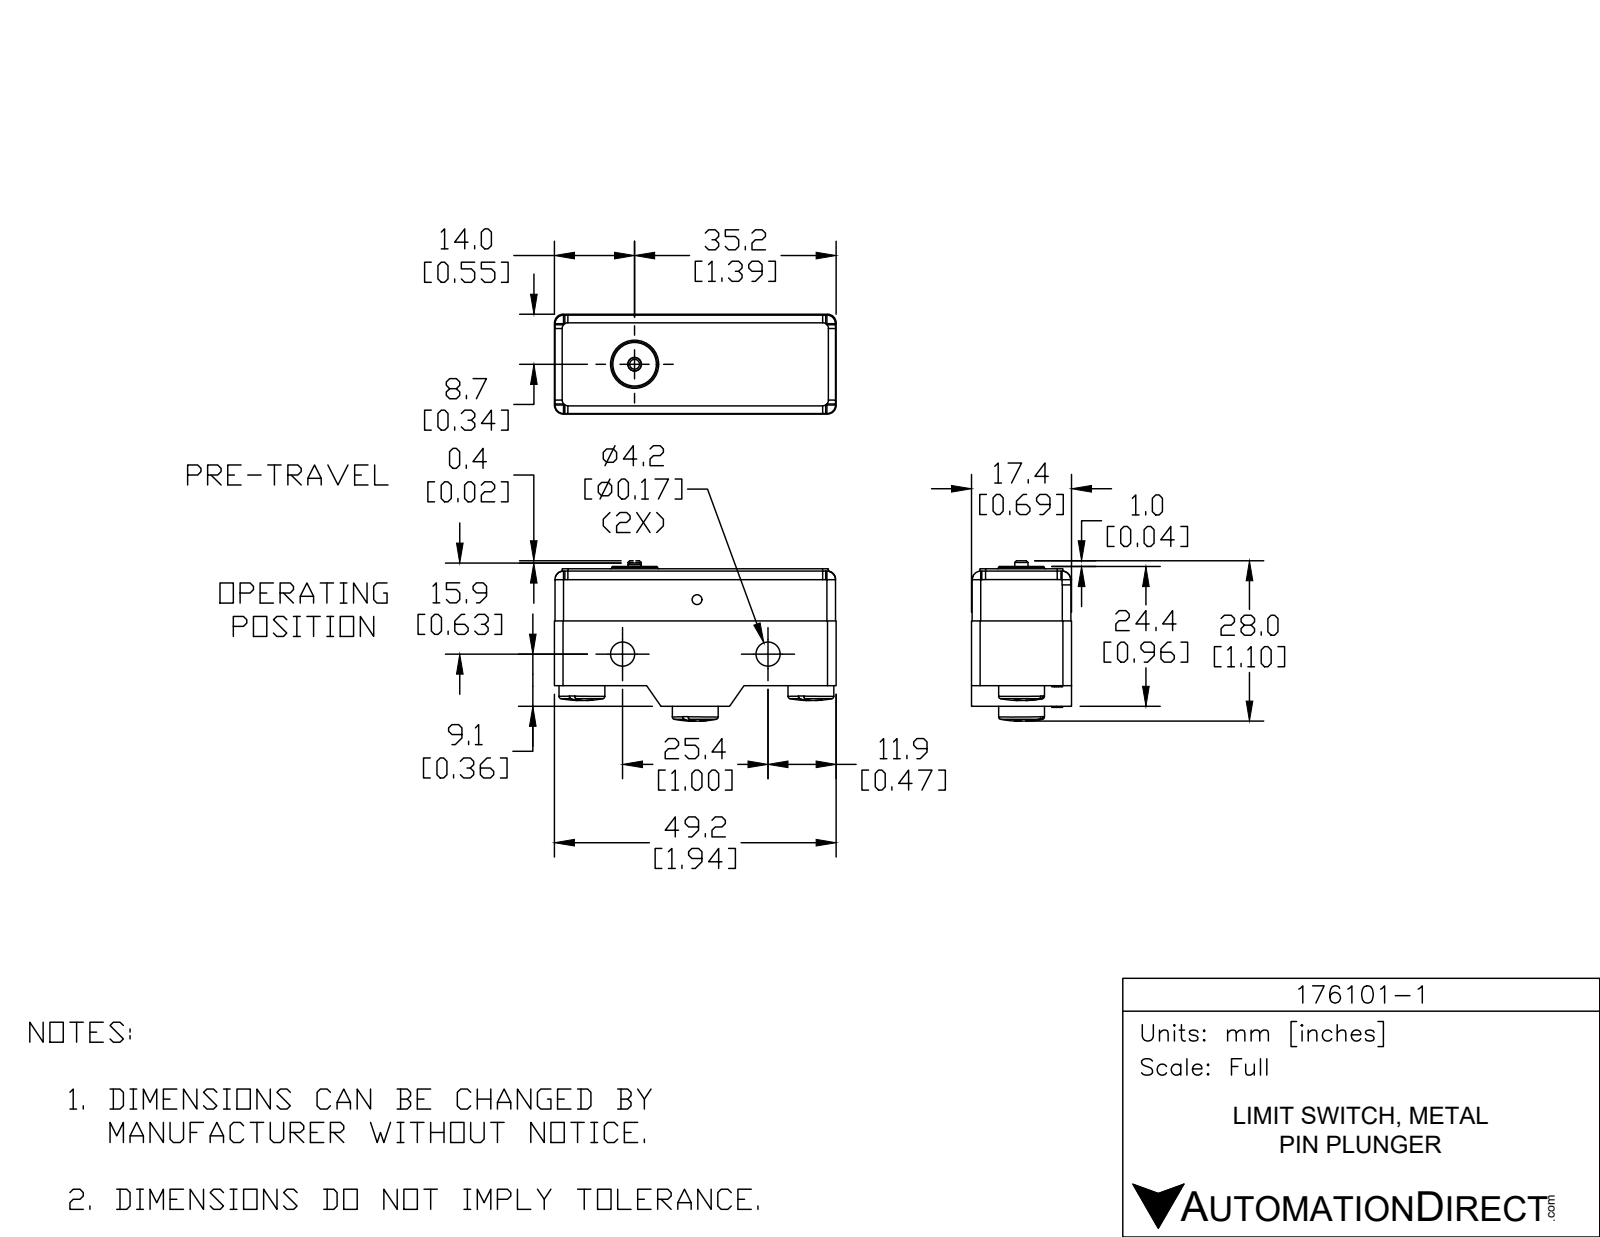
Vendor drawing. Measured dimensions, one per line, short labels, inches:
name: 176-MS (Screw Terminal)-Pin Plunger
written by: SolidWorks 2018 (AUTOMOTIVE_DESIGN)
unit: in
bodies: 2 solids, 464 faces (218 planar, 82 cylindrical, 164 other)
size: 1.937 × 1.102 × 0.687
volume: 1.03 in³; area: 9.454 in²
holes: 3× ⌀0.236, 2× ⌀0.165, 1× ⌀0.067, 1× ⌀0.094
bosses: 3× ⌀0.315, 3× ⌀0.15, 1× ⌀0.091
rounds: 18× R0.059, 12× R0.012, 4× R0.039, 3× R0.116
face distances: 0.683, 0.687, 0.803, 0.68, 1.933, 0.142, 0.945, 1.937, 1.929, 0.587
hole spacings: 0.362, 0.417, 0.615, 0.634, 0.78, 0.795, 1, 1.213
